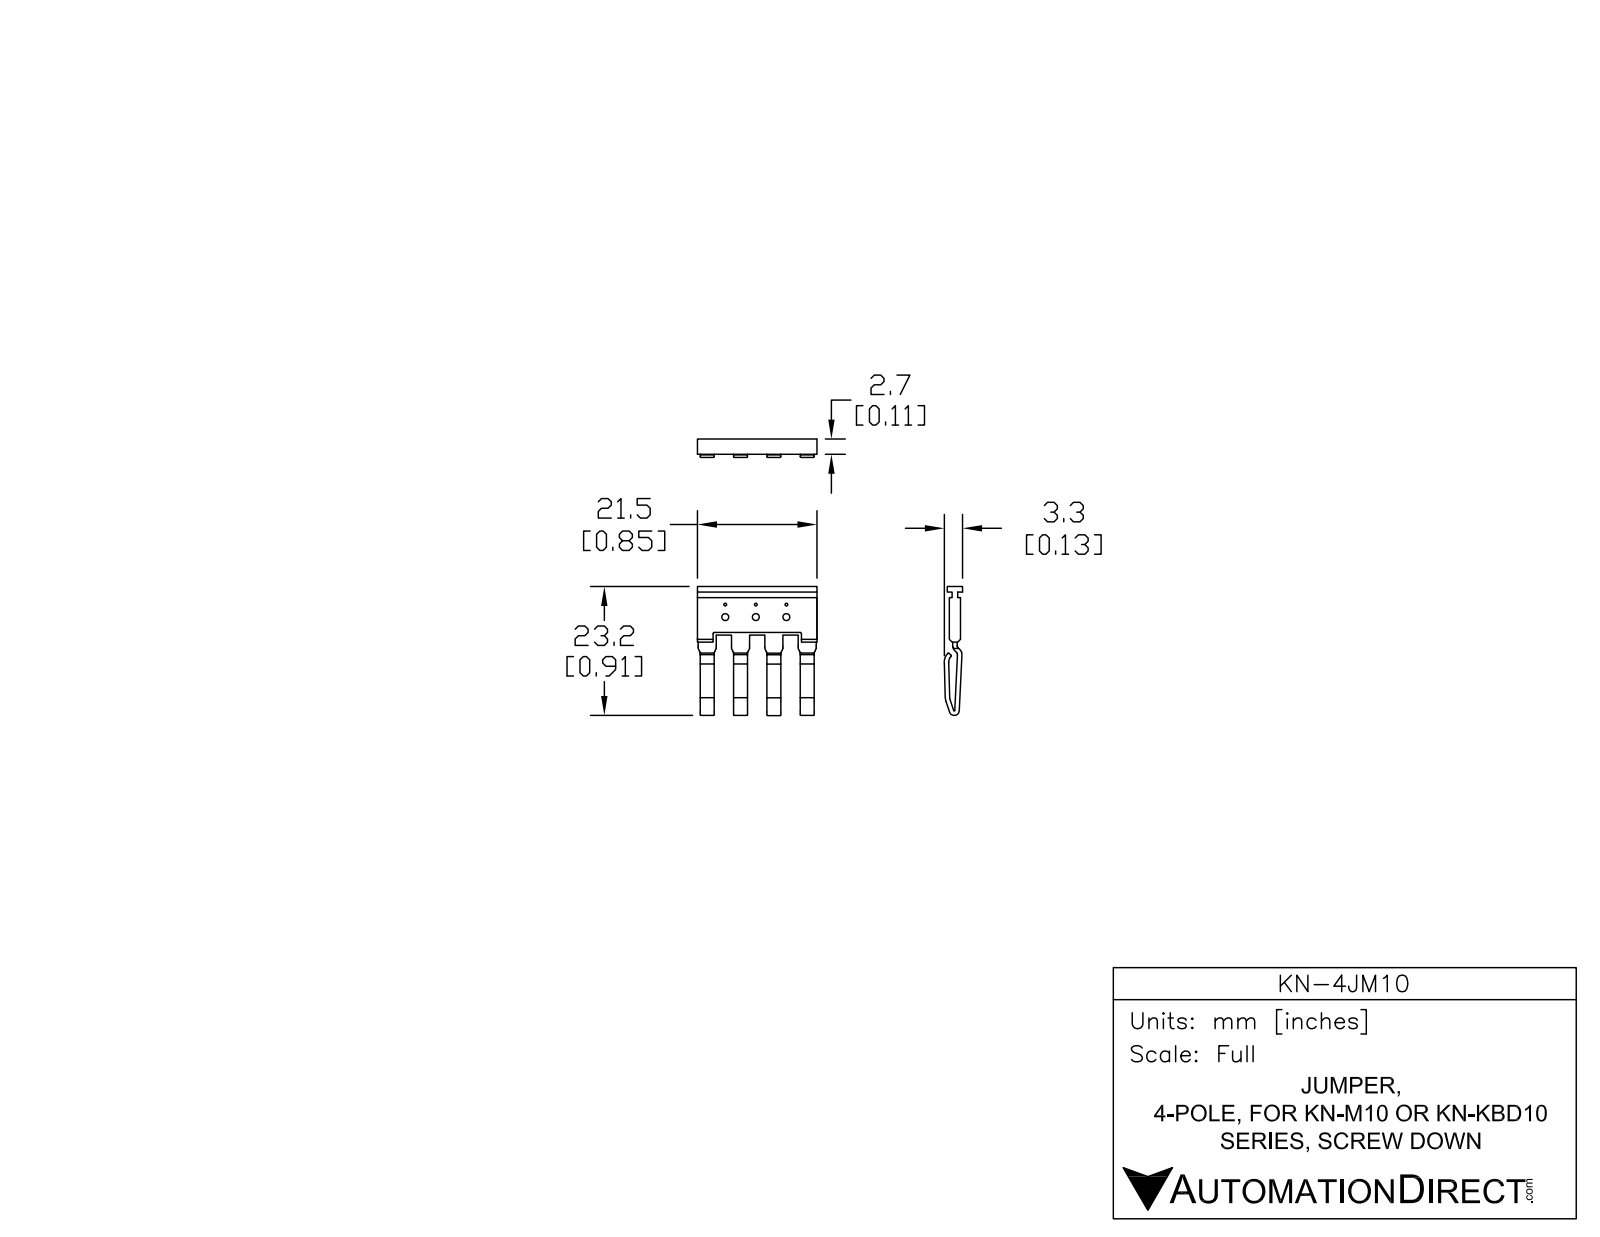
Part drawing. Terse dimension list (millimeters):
name: KN-4JM10
written by: SolidWorks 2014 (AUTOMOTIVE_DESIGN)
unit: mm
bodies: 2 solids, 421 faces (108 planar, 173 cylindrical, 140 other)
size: 23.19 × 21.5 × 3.3
volume: 583 mm³; area: 1 303 mm²
holes: 3× ⌀0.5, 3× ⌀1.25
rounds: 98× R0.12, 2× R0.25, 2× R0.6, 2× R1.4, 2× R1.6, 2× R2.4, 1× R0.1, 1× R0.9
face distances: 2, 0.8, 6, 1, 0.5, 0.6, 1.4, 12, 2.5, 1.5
hole spacings: 6, 6.41, 2.25, 12, 12.21
